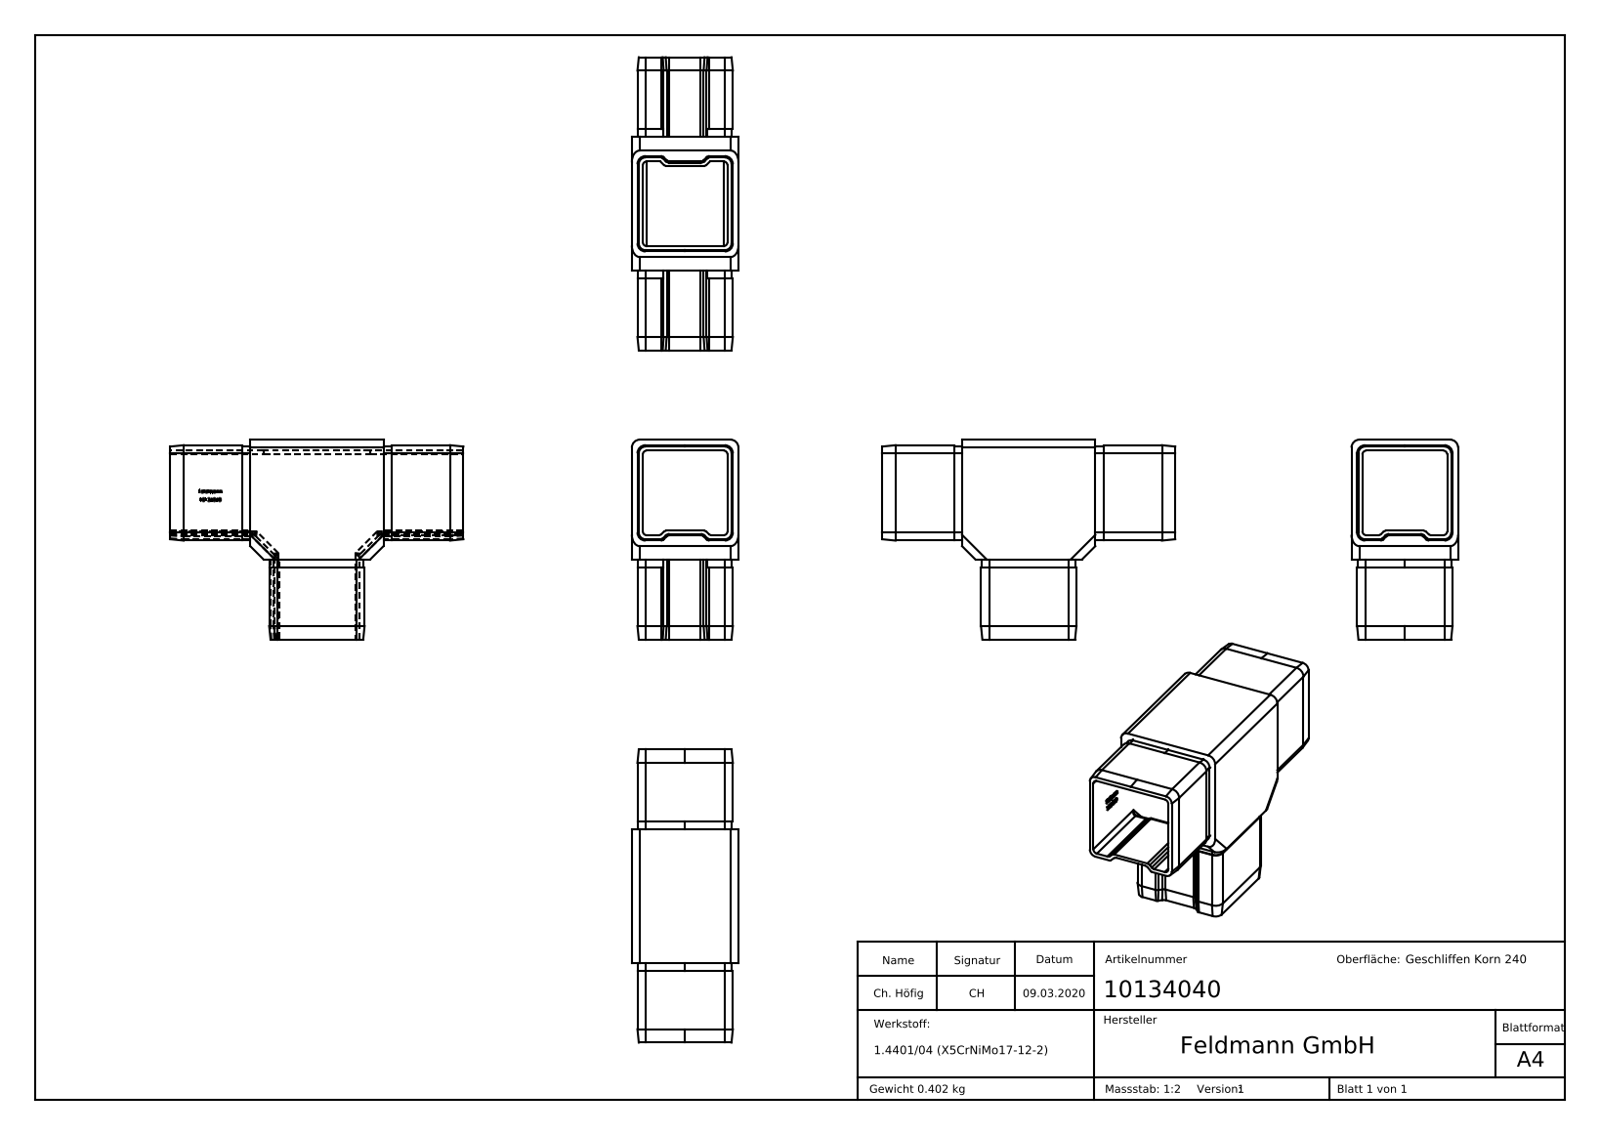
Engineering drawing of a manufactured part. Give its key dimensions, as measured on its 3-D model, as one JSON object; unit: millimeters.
{"part_name": "10134040", "step_written_by": "SolidWorks 2015 (CONFIG_CONTROL_DESIGN)", "units": "millimeters", "bodies": {"solids": 1, "faces": 467, "planar": 250, "cylindrical": 86, "other": 131}, "overall_size": [110, 75, 40], "volume_mm3": 50240, "surface_area_mm2": 38816, "partial_cylinders_radius": [[1.5, 39], [3, 14], [2.7, 8]], "face_to_face_distances": [2, 33.8, 31.8, 4.1, 2.1, 35.9, 37.9, 35.8, 1.7, 40]}
